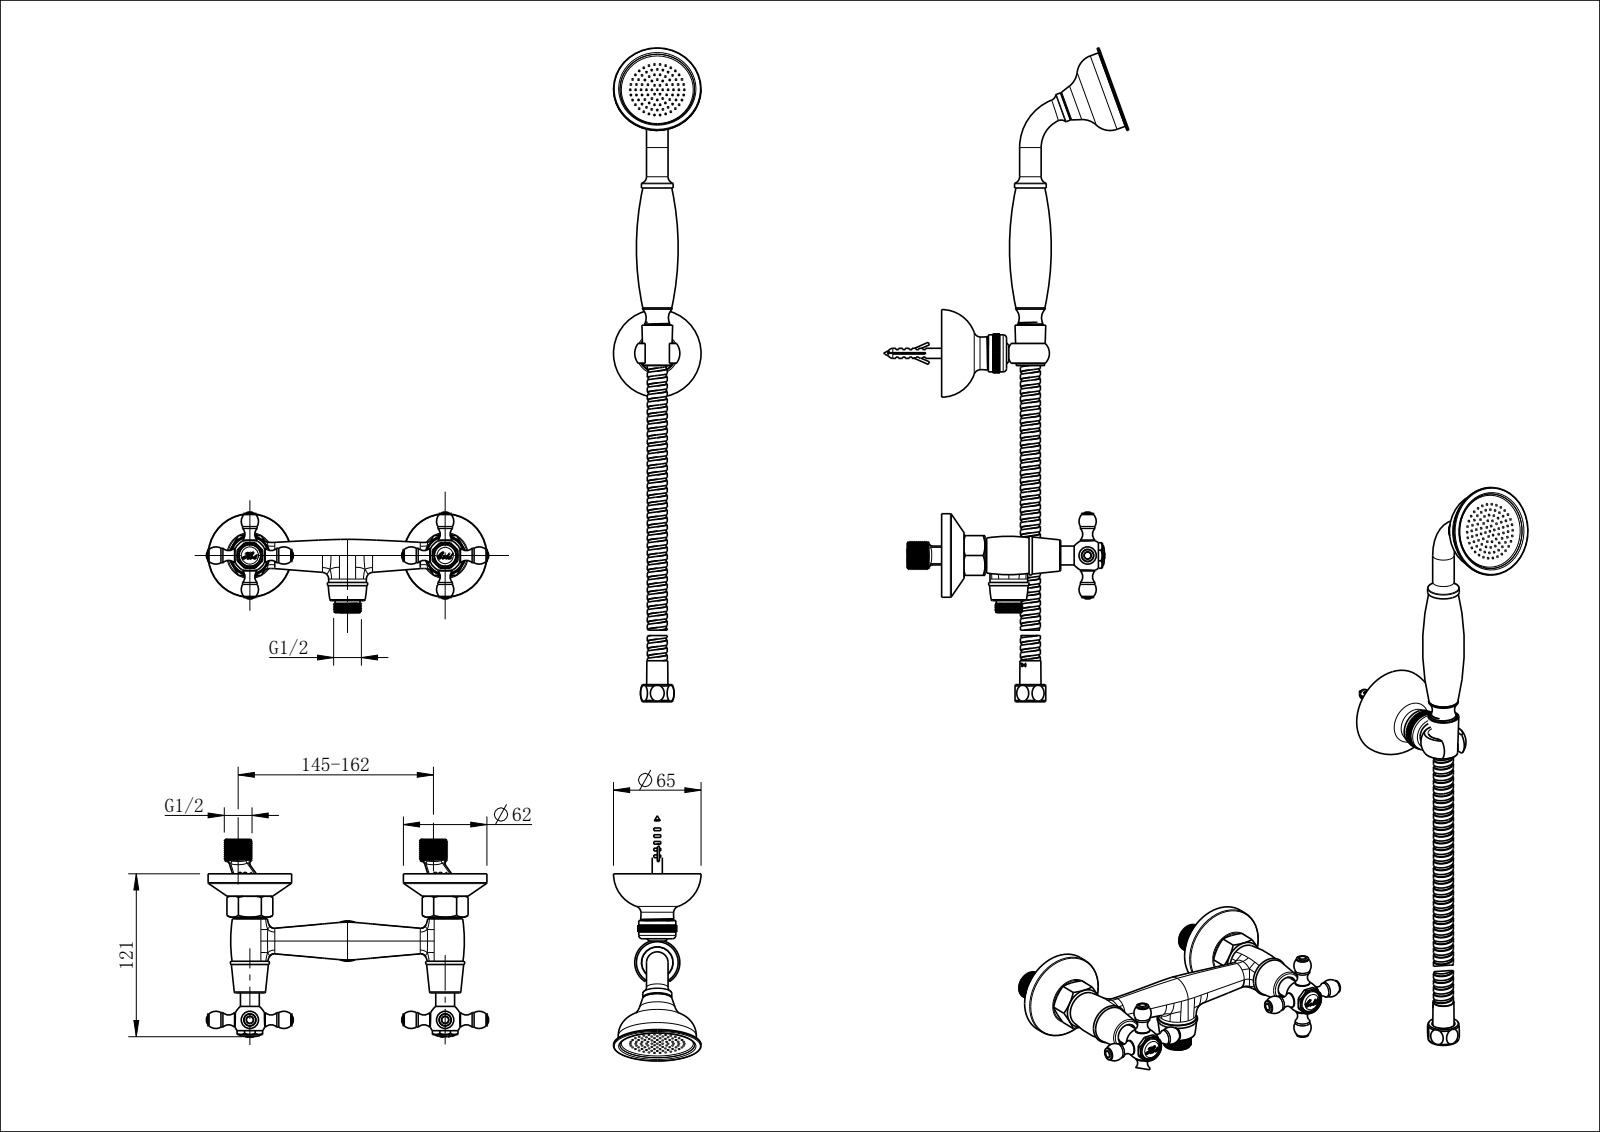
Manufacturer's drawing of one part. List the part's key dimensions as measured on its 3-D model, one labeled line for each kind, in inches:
Part name (STEP PRODUCT): MSBR-96; MSBR-95; MSBR-94; MSBR-93 (+8 more)
STEP written by: CREO PARAMETRIC BY PTC INC, 2015480 (AUTOMOTIVE_DESIGN)
Units: inches
Bodies: 96 solids, 7375 faces (2503 planar, 2822 cylindrical, 2050 other)
Overall size (bounding box): 48.803 × 33.006 × 8.967
Volume: 140.1 in³ · Surface area: 953 in²
Round holes (diameter × count): ⌀0.039 ×362, ⌀0.591 ×6, ⌀0.118 ×5, ⌀0.65 ×5, ⌀0.827 ×5, ⌀0.13 ×4, ⌀0.197 ×4, ⌀0.866 ×4, ⌀0.177 ×3, ⌀0.189 ×3, ⌀0.307 ×3, ⌀0.315 ×3
Round bosses / shafts (diameter × count): ⌀0.118 ×271, ⌀0.295 ×9, ⌀0.354 ×8, ⌀0.425 ×6, ⌀0.811 ×5, ⌀0.945 ×4, ⌀0.807 ×4, ⌀0.709 ×4
Partial cylindrical surfaces — rounded edges, fillets, slot ends (radius × count): R0.008 ×40, R0.039 ×18, R0.02 ×8, R0.118 ×8, R0.059 ×6, R0.098 ×5, R0.012 ×4, R0.031 ×4
Main face-to-face distances: 0.039, 0.079, 0.276, 0.394, 0.472, 0.551, 0.197, 1.063, 1.181, 0.63
Hole centre spacings: 0.752, 0.995, 0.316, 0.376, 0.474, 1.128, 0.651, 0.418
